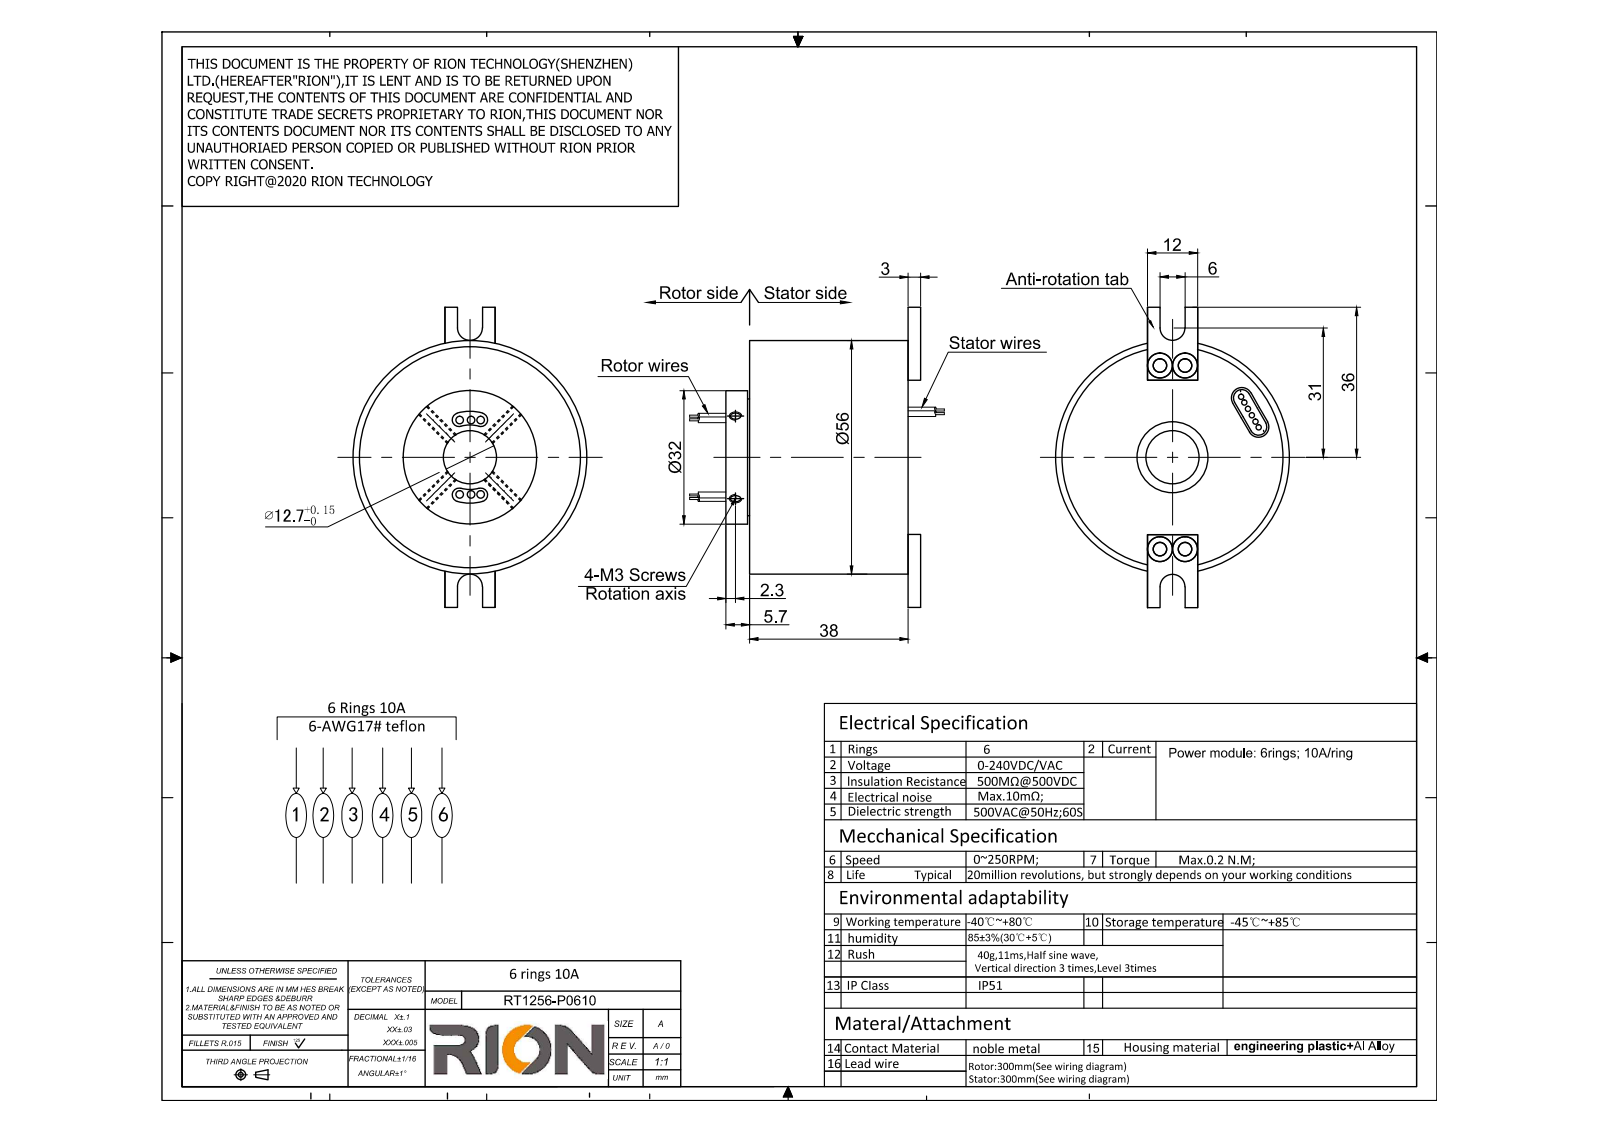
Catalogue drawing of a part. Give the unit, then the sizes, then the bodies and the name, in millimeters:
Units: millimetres
Overall size (bounding box): 72 × 62.2 × 56
Round holes (diameter × count): ⌀2.5 ×6, ⌀3.2 ×4, ⌀12.7 ×1, ⌀15.8 ×1, ⌀53 ×1
Round bosses / shafts (diameter × count): ⌀1.8 ×12, ⌀56 ×1, ⌀52.9 ×1, ⌀52.8 ×1, ⌀32 ×1, ⌀28 ×1, ⌀15.5 ×1
Partial cylindrical surfaces — rounded edges, fillets, slot ends (radius × count): R1.62 ×4, R2 ×2, R3 ×2, R8.12 ×1, R11.38 ×1
Main face-to-face distances: 38, 5.7, 43.7, 3, 46.7, 41, 5, 0.7, 38.7, 41.7
Hole centre spacings: 22.7, 6, 45, 45.4
Volume: 93 203 mm³ · Surface area: 17 738 mm²
Bodies: 1 solid, 155 faces (56 planar, 83 cylindrical, 16 other)
Part name (STEP PRODUCT): Admi28DCE49Ak8dx
STEP written by: SIEMENS PLM Software NX 8.5 (AUTOMOTIVE_DESIGN)
